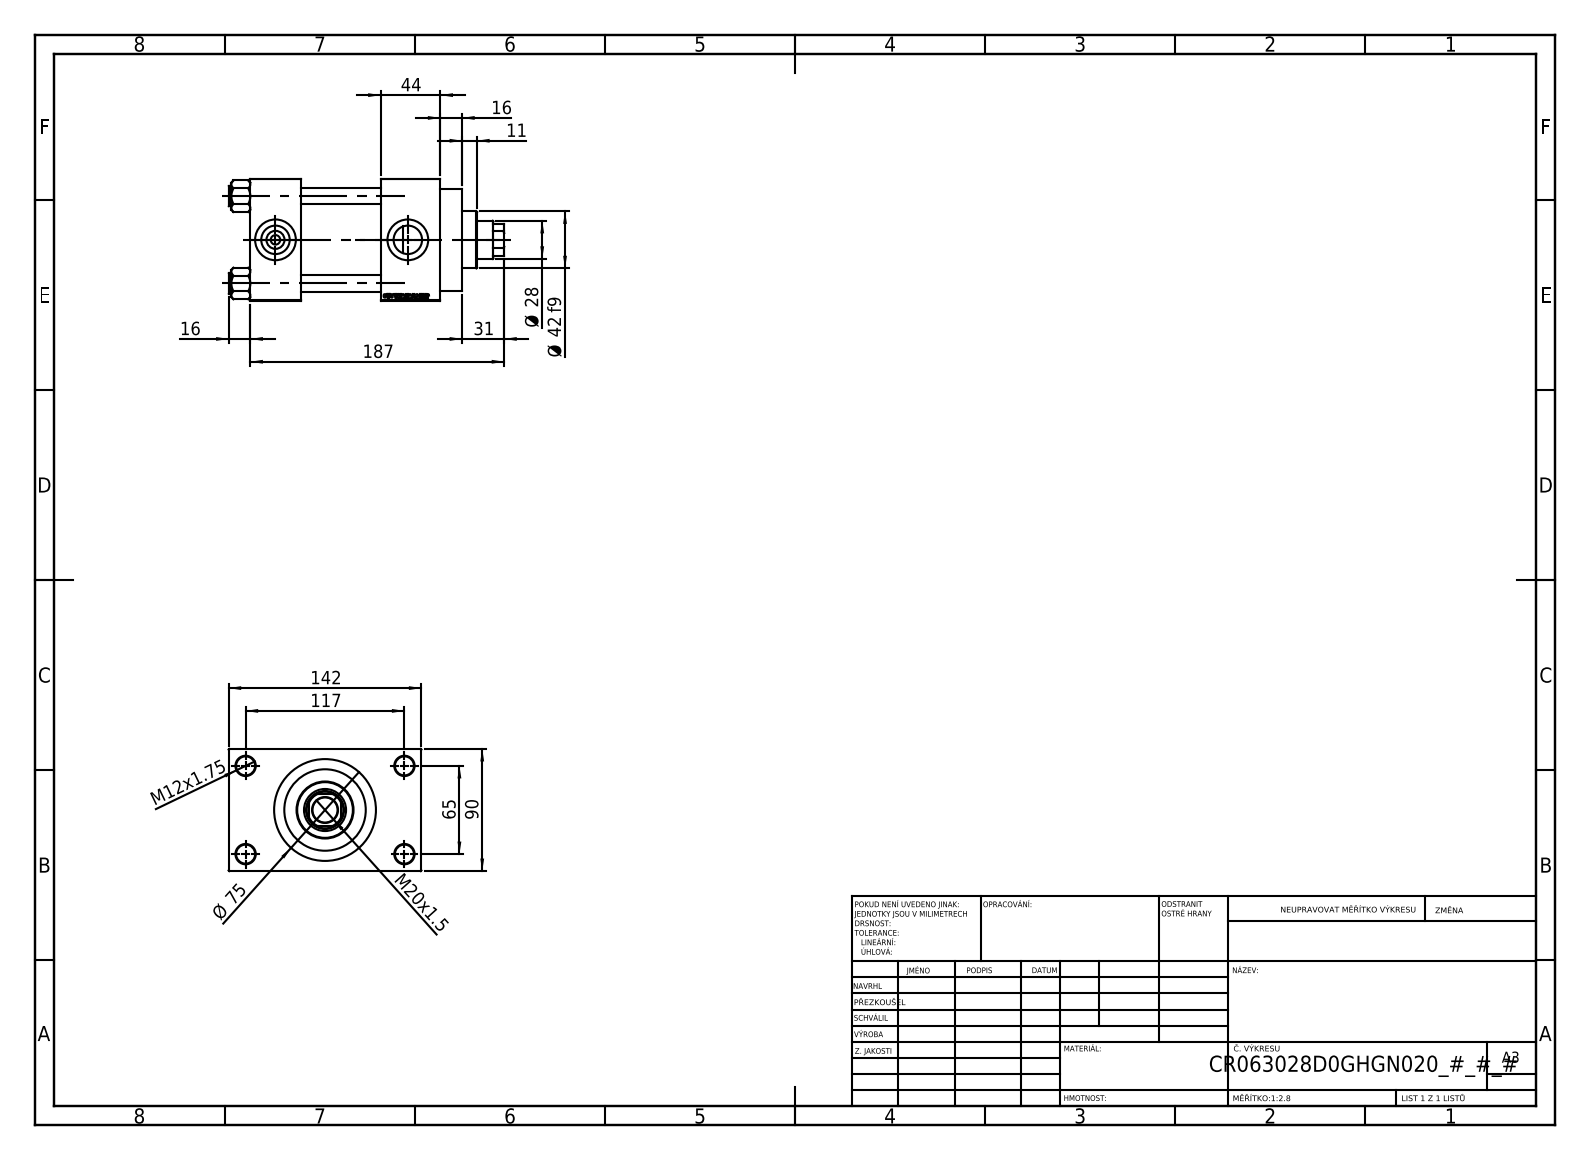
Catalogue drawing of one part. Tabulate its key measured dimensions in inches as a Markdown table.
| quantity | value |
| --- | --- |
| part name | V215CR_D_Body; V215_VC_A; V215CR_D_TYCINKA; V215CR_VCP_D (+1 more) |
| STEP written by | SolidWorks 2019 (CONFIG_CONTROL_DESIGN) |
| units | inches |
| bodies | 11 solids, 1103 faces (497 planar, 88 cylindrical, 518 other) |
| overall size | 7.992 × 5.591 × 3.543 |
| volume | 66.88 in³ |
| surface area | 310.5 in² |
| round holes (diameter × count) | 0.472 × 4, 0.551 × 4, 0.276 × 2, 0.825 × 2, 1.181 × 2, 0.728 × 1, 1.102 × 1, 1.22 × 1, 1.969 × 1, 2.362 × 1, 2.48 × 1 |
| round bosses / shafts (diameter × count) | 0.591 × 4, 2.953 × 1, 2.717 × 1, 1.654 × 1 |
| partial cylindrical surfaces (radius × count) | 0.531 × 1 |
| main face-to-face distances | 3.543, 2.323, 1.457, 3.78, 5.512, 4.055, 1.732, 1.024, 4.567, 0.63 |
| hole center spacings | 1.037, 1.79, 2.531, 2.635, 2.748, 3.569, 4.383, 2.559 |
